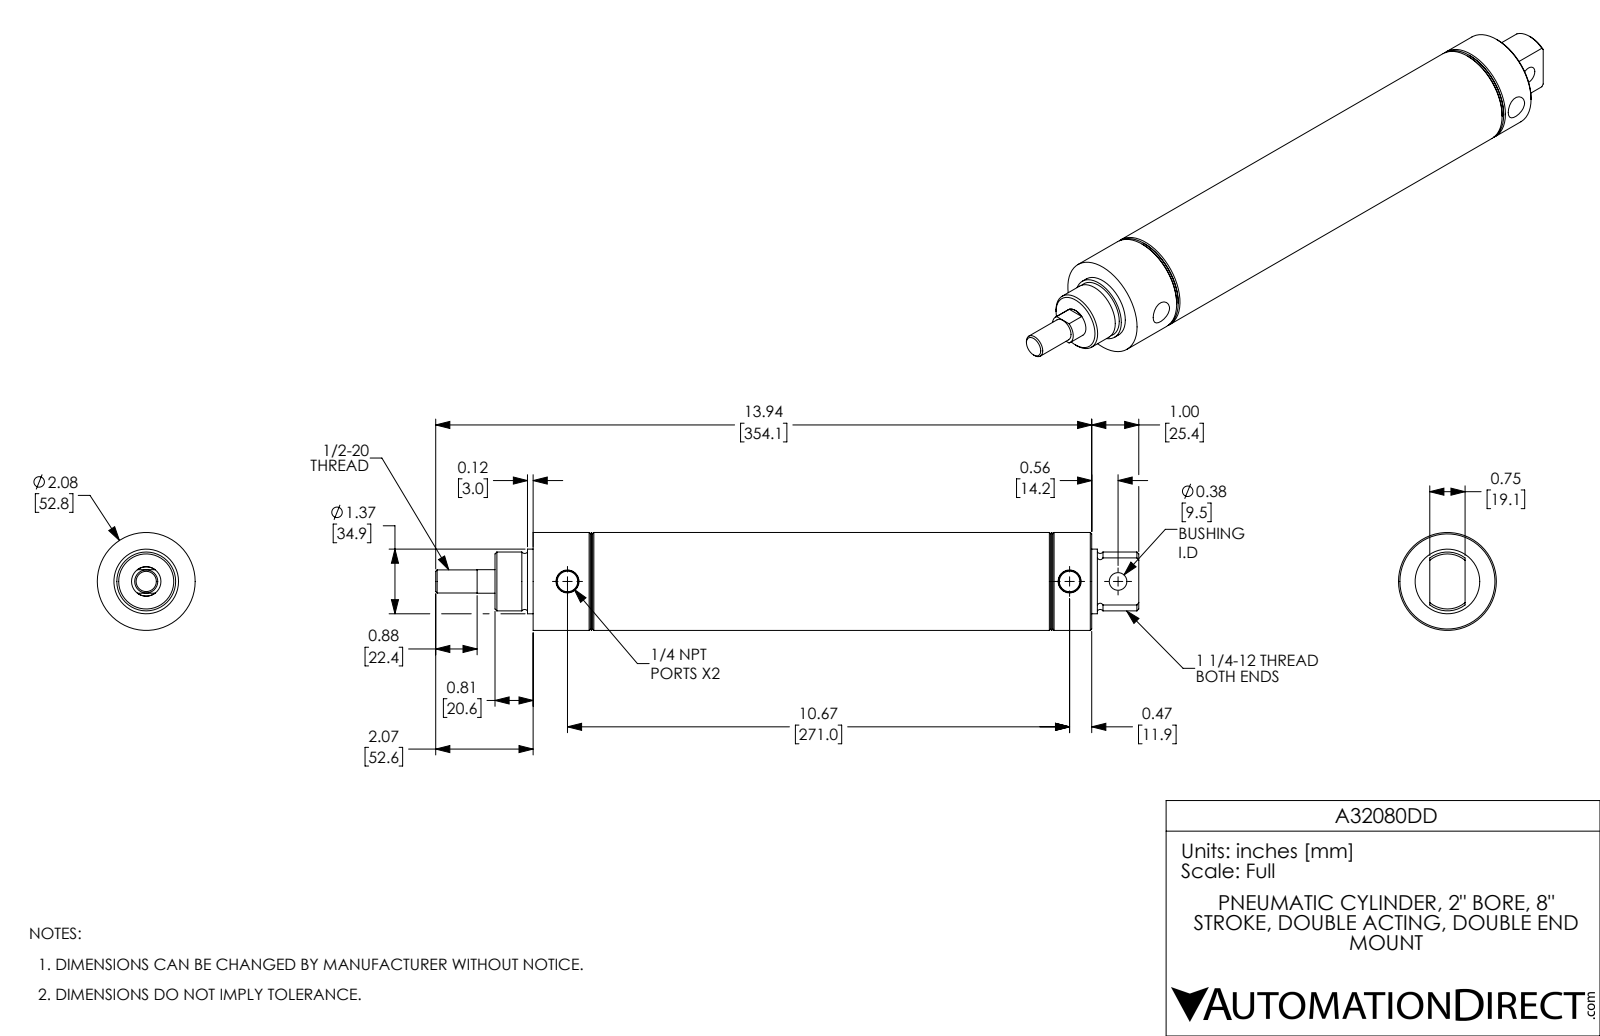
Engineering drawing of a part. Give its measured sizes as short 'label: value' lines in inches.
name: A32080DD-MainBody; A32080DD-Rod; A32080DD
written by: SolidWorks 2017 (AUTOMOTIVE_DESIGN)
unit: in
bodies: 2 solids, 88 faces (20 planar, 30 cylindrical, 38 other)
size: 14.94 × 2.08 × 2.08
volume: 19.49 in³; area: 190.5 in²
holes: 2× ⌀0.438, 1× ⌀0.375, 1× ⌀0.625, 1× ⌀2
bosses: 1× ⌀2.08, 1× ⌀1.373, 1× ⌀1.25, 1× ⌀0.491
face distances: 0.5, 8.5, 8, 10.185, 9.685, 1.685, 1.685, 2.185, 10.185, 11.87
hole spacings: 1.03, 10.67, 11.7
